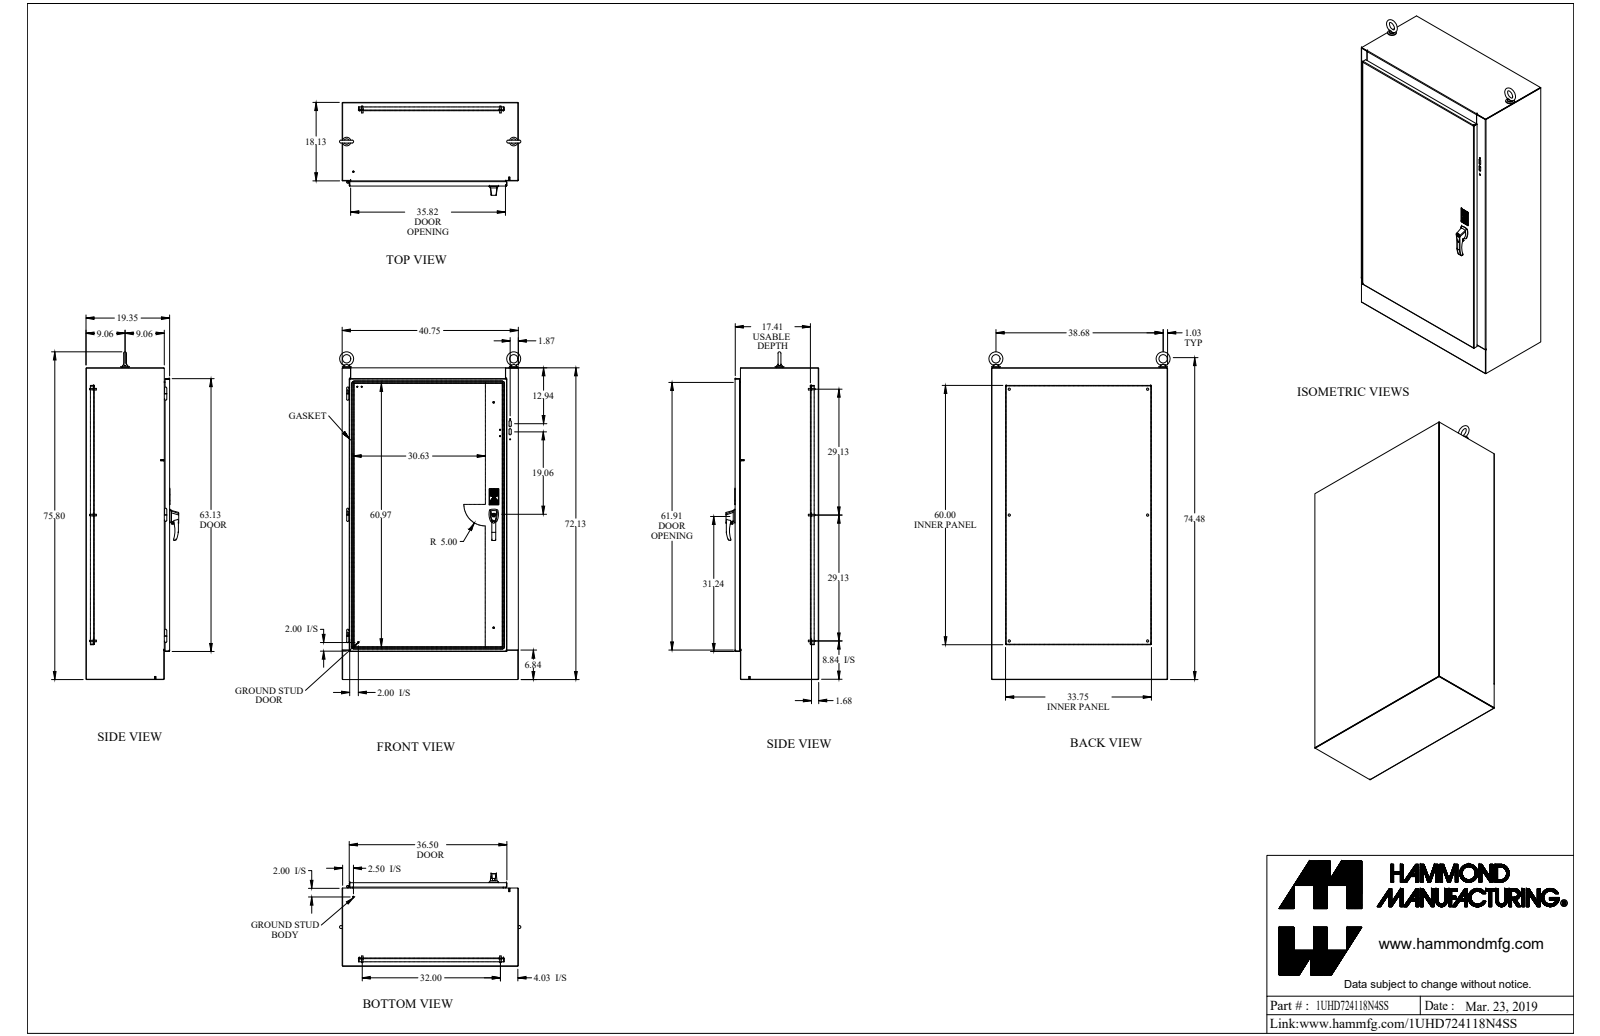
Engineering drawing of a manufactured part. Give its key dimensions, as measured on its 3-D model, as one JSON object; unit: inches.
{"part_name": "1UHD724118N4SS", "step_written_by": "SolidWorks 2018 (AUTOMOTIVE_DESIGN)", "units": "inches", "bodies": {"solids": 112, "faces": 2003, "planar": 1132, "cylindrical": 535, "other": 336}, "overall_size": [75.799, 41.932, 21.464], "volume_in3": 1420, "surface_area_in2": 28300, "round_holes": [[0.35, 7], [0.196, 6], [0.307, 6], [0.563, 6], [0.25, 5], [0.156, 4], [0.281, 4], [0.445, 4], [0.313, 3], [0.167, 2], [0.189, 2], [0.255, 2]], "round_bosses_or_shafts": [[0.25, 11], [1, 8], [0.65, 6], [0.375, 6], [0.332, 6], [0.19, 4], [0.625, 3], [0.5, 3]], "partial_cylinders_radius": [[0.125, 27], [0.048, 24], [0.143, 24], [0.5, 23], [0.06, 19], [0.25, 19], [0.017, 16], [0.032, 12]], "face_to_face_distances": [0.095, 19.254, 40.655, 19.159, 19.349, 0.125, 1.907, 1.812, 17.348, 17.443], "hole_center_spacings": [43.27, 32, 7.433, 7.467, 7.5, 7.735, 12.875, 14.9]}
